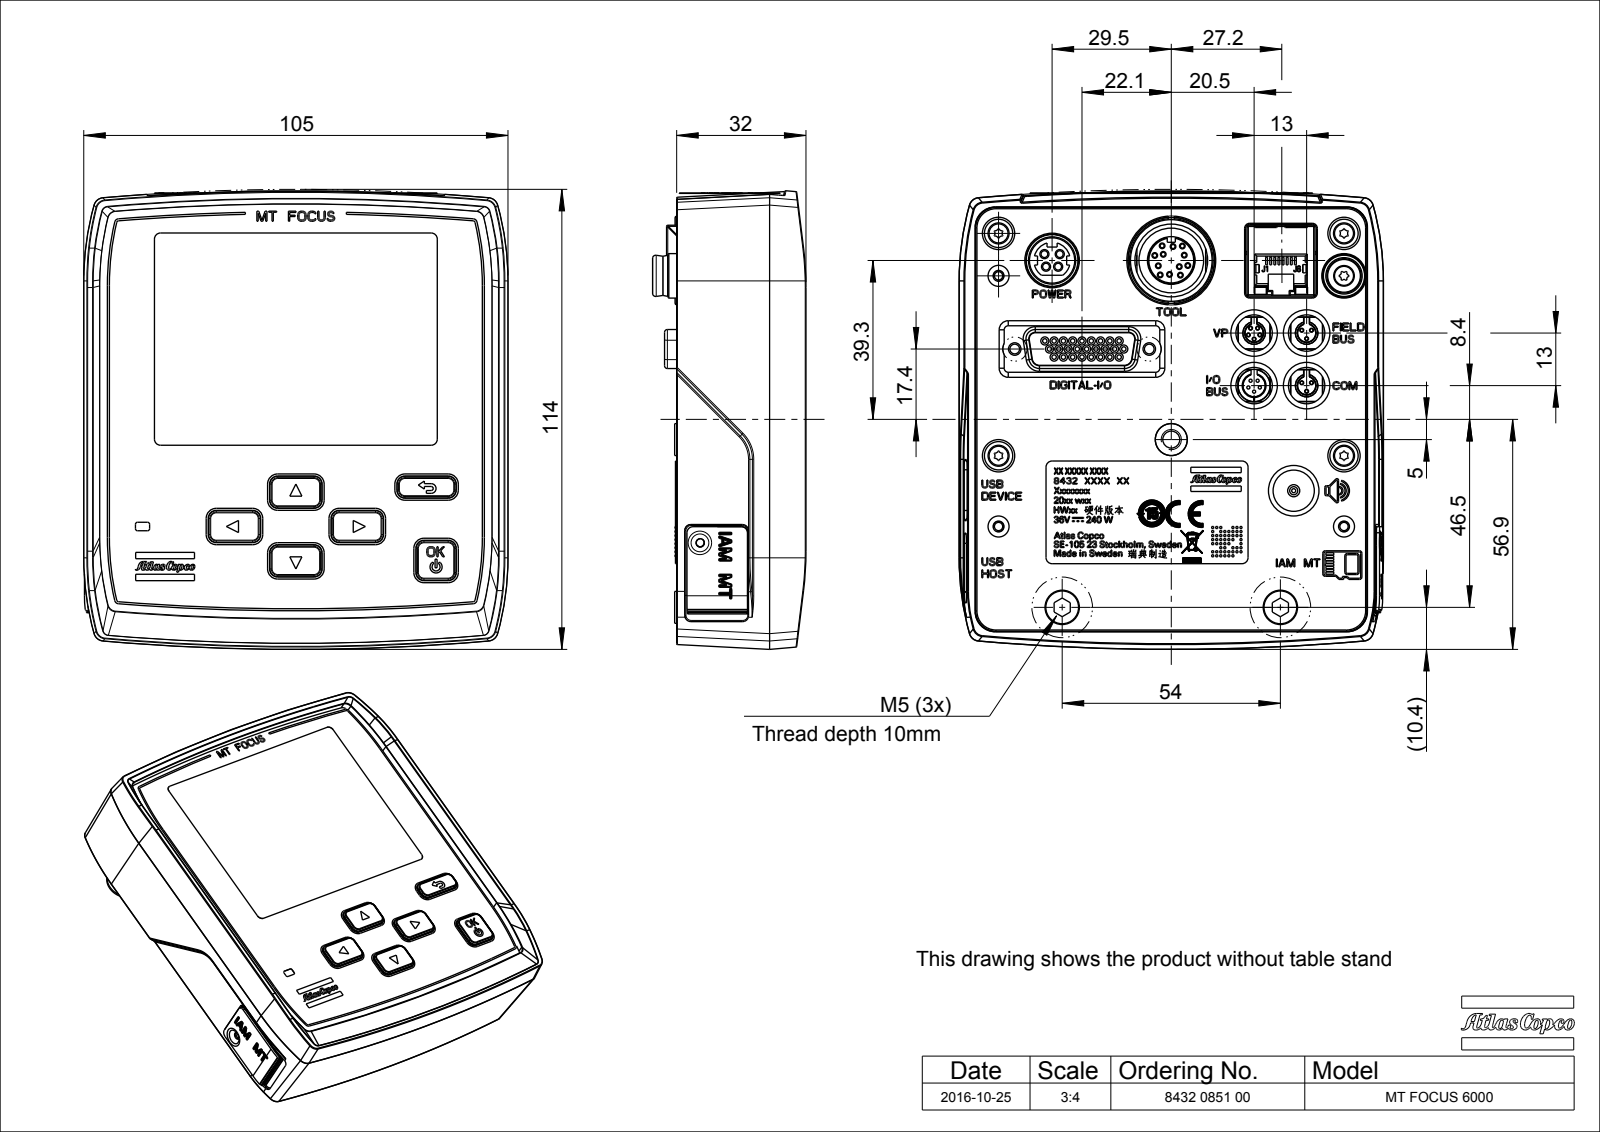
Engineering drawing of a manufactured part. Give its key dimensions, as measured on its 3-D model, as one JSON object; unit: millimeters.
{"part_name": "4216262500_AF0; 0298100175; 4216262580_AF0_ASM; 0219110030 (+8 more)", "step_written_by": "CREO PARAMETRIC BY PTC INC, 2015380 (CONFIG_CONTROL_DESIGN)", "units": "millimeters", "bodies": {"solids": 37, "faces": 5480, "planar": 2477, "cylindrical": 1630, "other": 1373}, "overall_size": [113.45, 105, 37.96], "volume_mm3": 120288, "surface_area_mm2": 111499, "round_holes": [[1.1, 43], [0.6, 16], [1, 12], [2.7, 8], [2.05, 7], [5, 6], [0.78, 5], [1.67, 4], [6.3, 4], [6.35, 4], [9, 4], [10.5, 4]], "round_bosses_or_shafts": [[0.78, 11], [4.7, 8], [2.5, 8], [2, 7], [13, 4], [7.5, 4], [2.88, 4], [11.1, 3]], "partial_cylinders_radius": [[0.1, 153], [0.25, 135], [0.15, 100], [0.5, 79], [0.3, 74], [1, 65], [0.2, 49], [0.84, 42]], "face_to_face_distances": [2, 25.8, 3, 26.8, 23.8, 28.8, 24.8, 4, 21.8, 1.6], "hole_center_spacings": [2.13, 2.71, 4.28, 5.15, 6.67, 13, 72.56, 85.5]}
